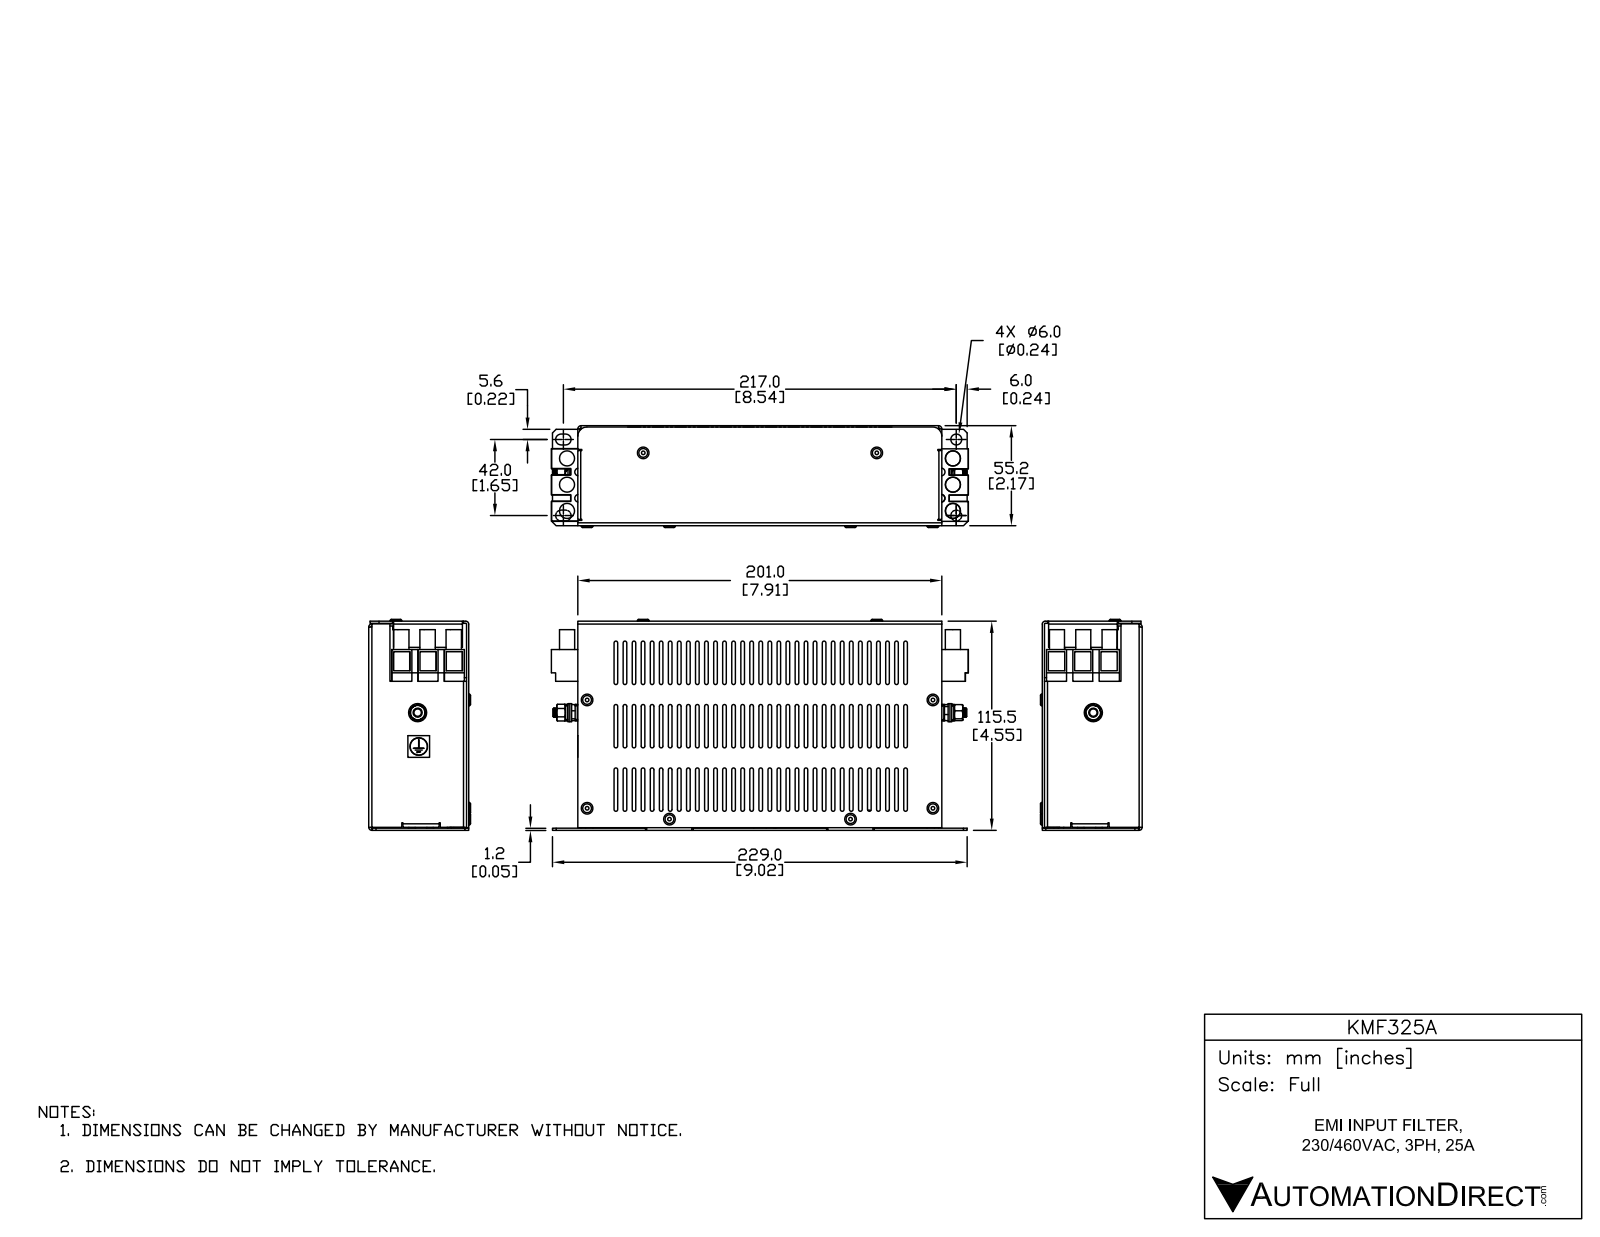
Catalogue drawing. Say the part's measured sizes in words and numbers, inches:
The part is named "KMF325A". Its 3-D file was written by "SolidWorks 2017 (AUTOMOTIVE_DESIGN)". It is 38 solids with 2428 faces: 1384 planar, 704 cylindrical and 340 other. Overall it measures 9.067 by 4.587 by 2.213 inches. Its volume is 10.46 cubic inches and its surface area 324.9 square inches. Round holes: 12 of diameter 0.079, 12 of diameter 0.138, 8 of diameter 0.13, 8 of diameter 0.169, 2 of diameter 0.154, 2 of diameter 0.236, 1 of diameter 0.051, 1 of diameter 0.165, 1 of diameter 0.165, 1 of diameter 0.205, 1 of diameter 0.383. Round bosses or shafts: 24 of diameter 0.327, 12 of diameter 0.138, 4 of diameter 0.252, 1 of diameter 0.394, 1 of diameter 0.373, 1 of diameter 0.315, 1 of diameter 0.307, 1 of diameter 0.268. Partial cylindrical surfaces (rounded edges, fillets, slot ends): 198 of radius 0.039, 18 of radius 0.02, 7 of radius 0.076, 6 of radius 0.067, 4 of radius 0.118, 3 of radius 0.016, 3 of radius 0.029, 3 of radius 0.063. The main face-to-face distances are 0.047, 2.126, 2.079, 4.5, 2.173, 4.547, 4.453, 7.866, 0.571, 0.059. The hole center spacings are 0.394, 2.354, 0.571, 1.224, 1.389, 1.807, 3.15, 5.733.
